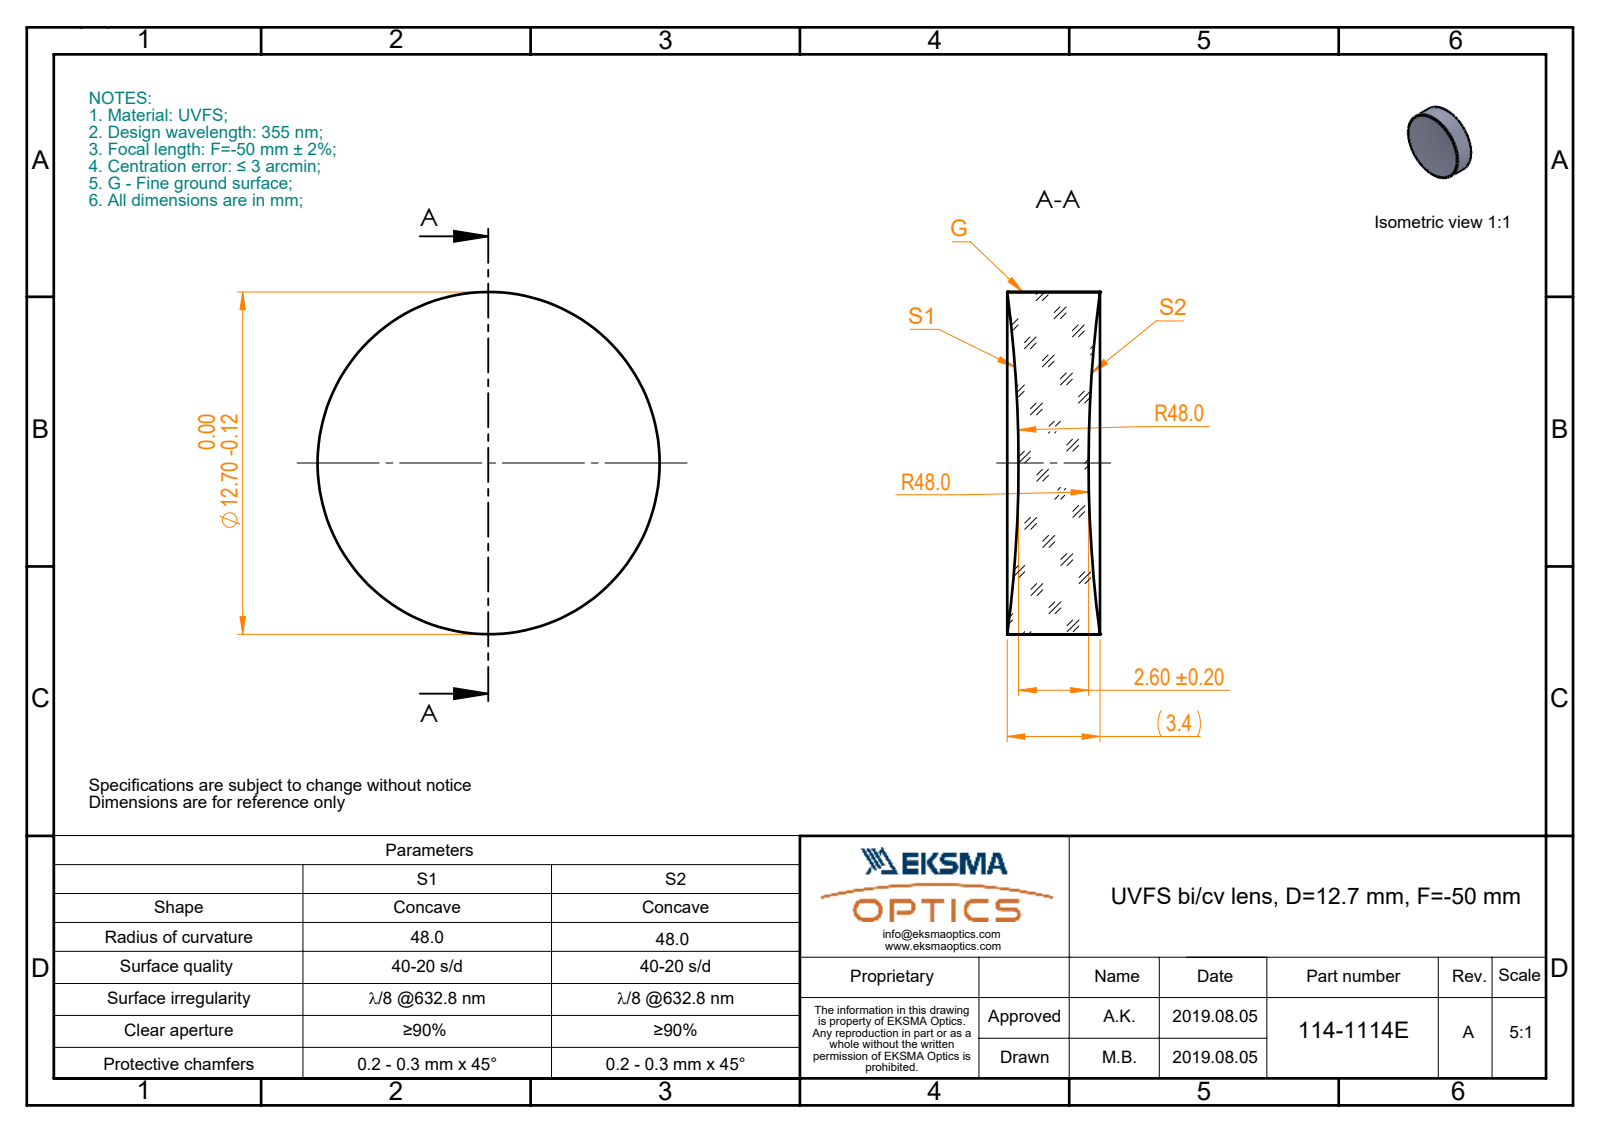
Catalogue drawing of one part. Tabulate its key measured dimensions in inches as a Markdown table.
| quantity | value |
| --- | --- |
| part name | 114-1114E UVFS bi-cv 12.7 F-50 |
| STEP written by | SolidWorks 2017 (CONFIG_CONTROL_DESIGN) |
| units | inches |
| bodies | 1 solid, 6 faces (0 planar, 2 cylindrical, 4 other) |
| overall size | 0.5 × 0.5 × 0.135 |
| volume | 0.023 in³ |
| surface area | 0.608 in² |
| round bosses / shafts (diameter × count) | 0.5 × 1 |
